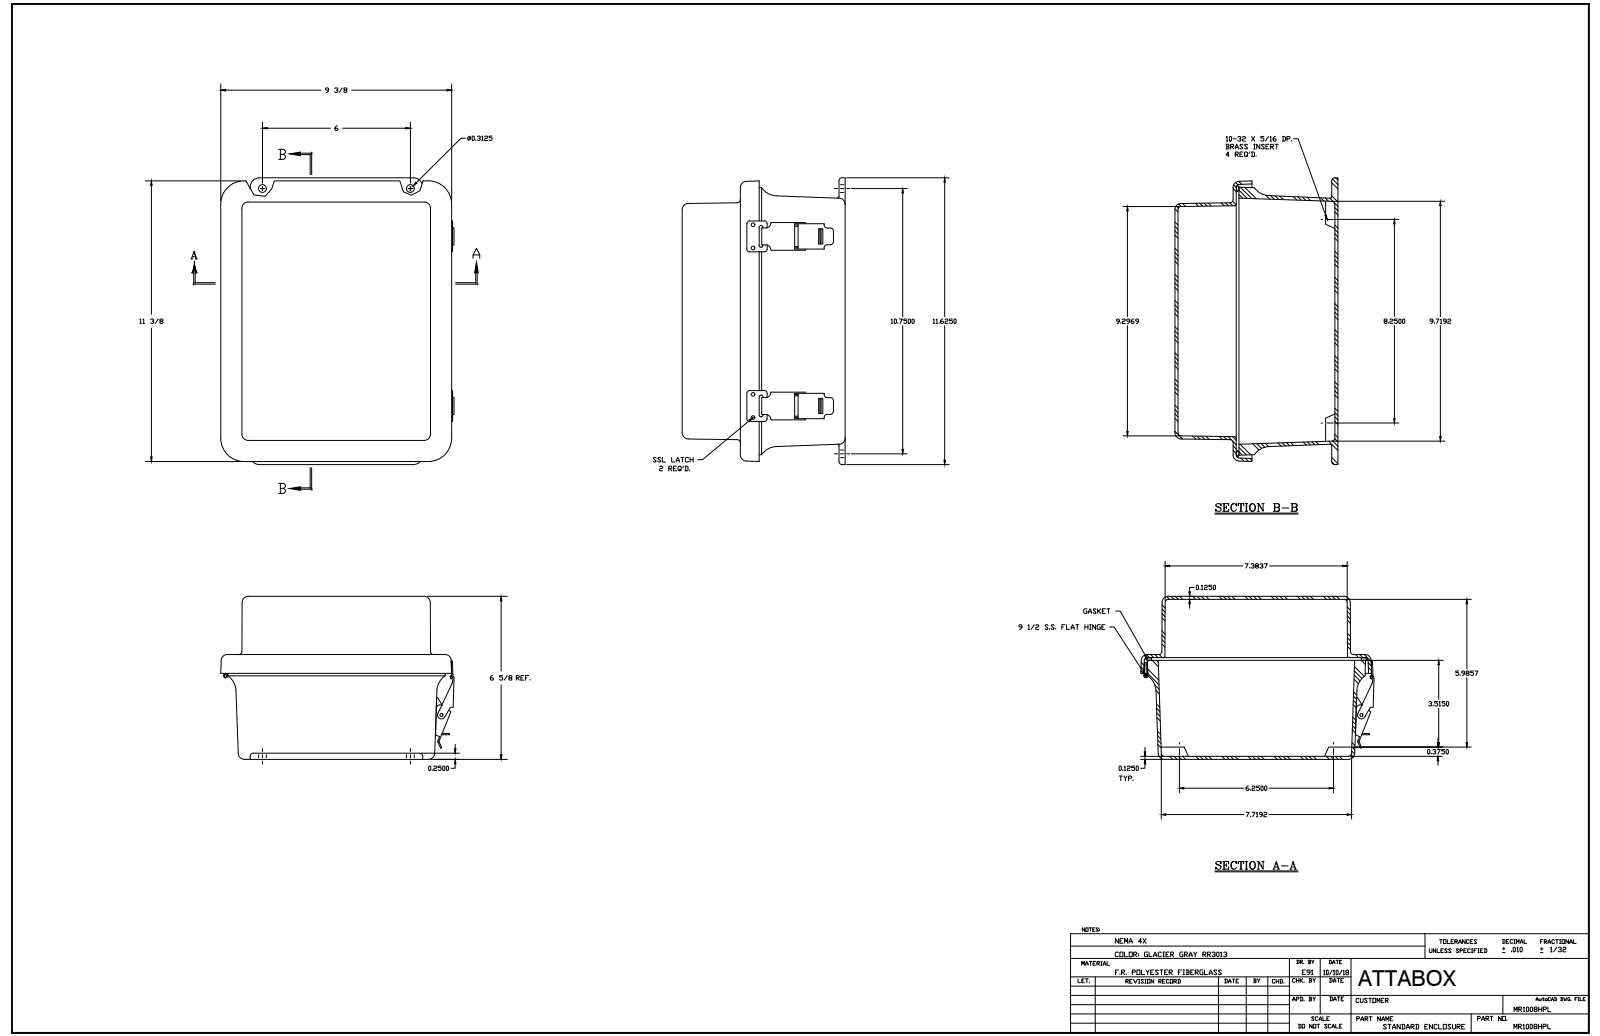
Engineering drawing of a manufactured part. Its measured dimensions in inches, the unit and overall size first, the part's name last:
Units: inches
Overall size (bounding box): 11.625 × 9.534 × 6.594
Round holes (diameter × count): ⌀0.14 ×20, ⌀0.104 ×8, ⌀0.131 ×8, ⌀0.152 ×5, ⌀0.13 ×4, ⌀0.156 ×4, ⌀0.218 ×4, ⌀0.135 ×2, ⌀0.375 ×2, ⌀0.085 ×1, ⌀0.085 ×1
Round bosses / shafts (diameter × count): ⌀0.125 ×13, ⌀0.25 ×8, ⌀0.27 ×4, ⌀0.125 ×3, ⌀0.3 ×1, ⌀0.17 ×1, ⌀0.155 ×1, ⌀0.135 ×1
Partial cylindrical surfaces — rounded edges, fillets, slot ends (radius × count): R0.125 ×32, R0.015 ×20, R0.031 ×20, R0.045 ×16, R0.03 ×12, R0.25 ×12, R0.023 ×8, R0.06 ×6
Main face-to-face distances: 0.125, 0.125, 6.344, 6.469, 6.594, 6.469, 4.109, 3.984, 2.36, 2.485
Hole centre spacings: 7, 7.04, 0.937, 6, 0.75, 3, 0.25, 0.75
Volume: 69.08 in³ · Surface area: 986.7 in²
Bodies: 38 solids, 989 faces (409 planar, 409 cylindrical, 171 other)
Part name (STEP PRODUCT): MR1008HPL
STEP written by: SolidWorks 2018 (AUTOMOTIVE_DESIGN)
